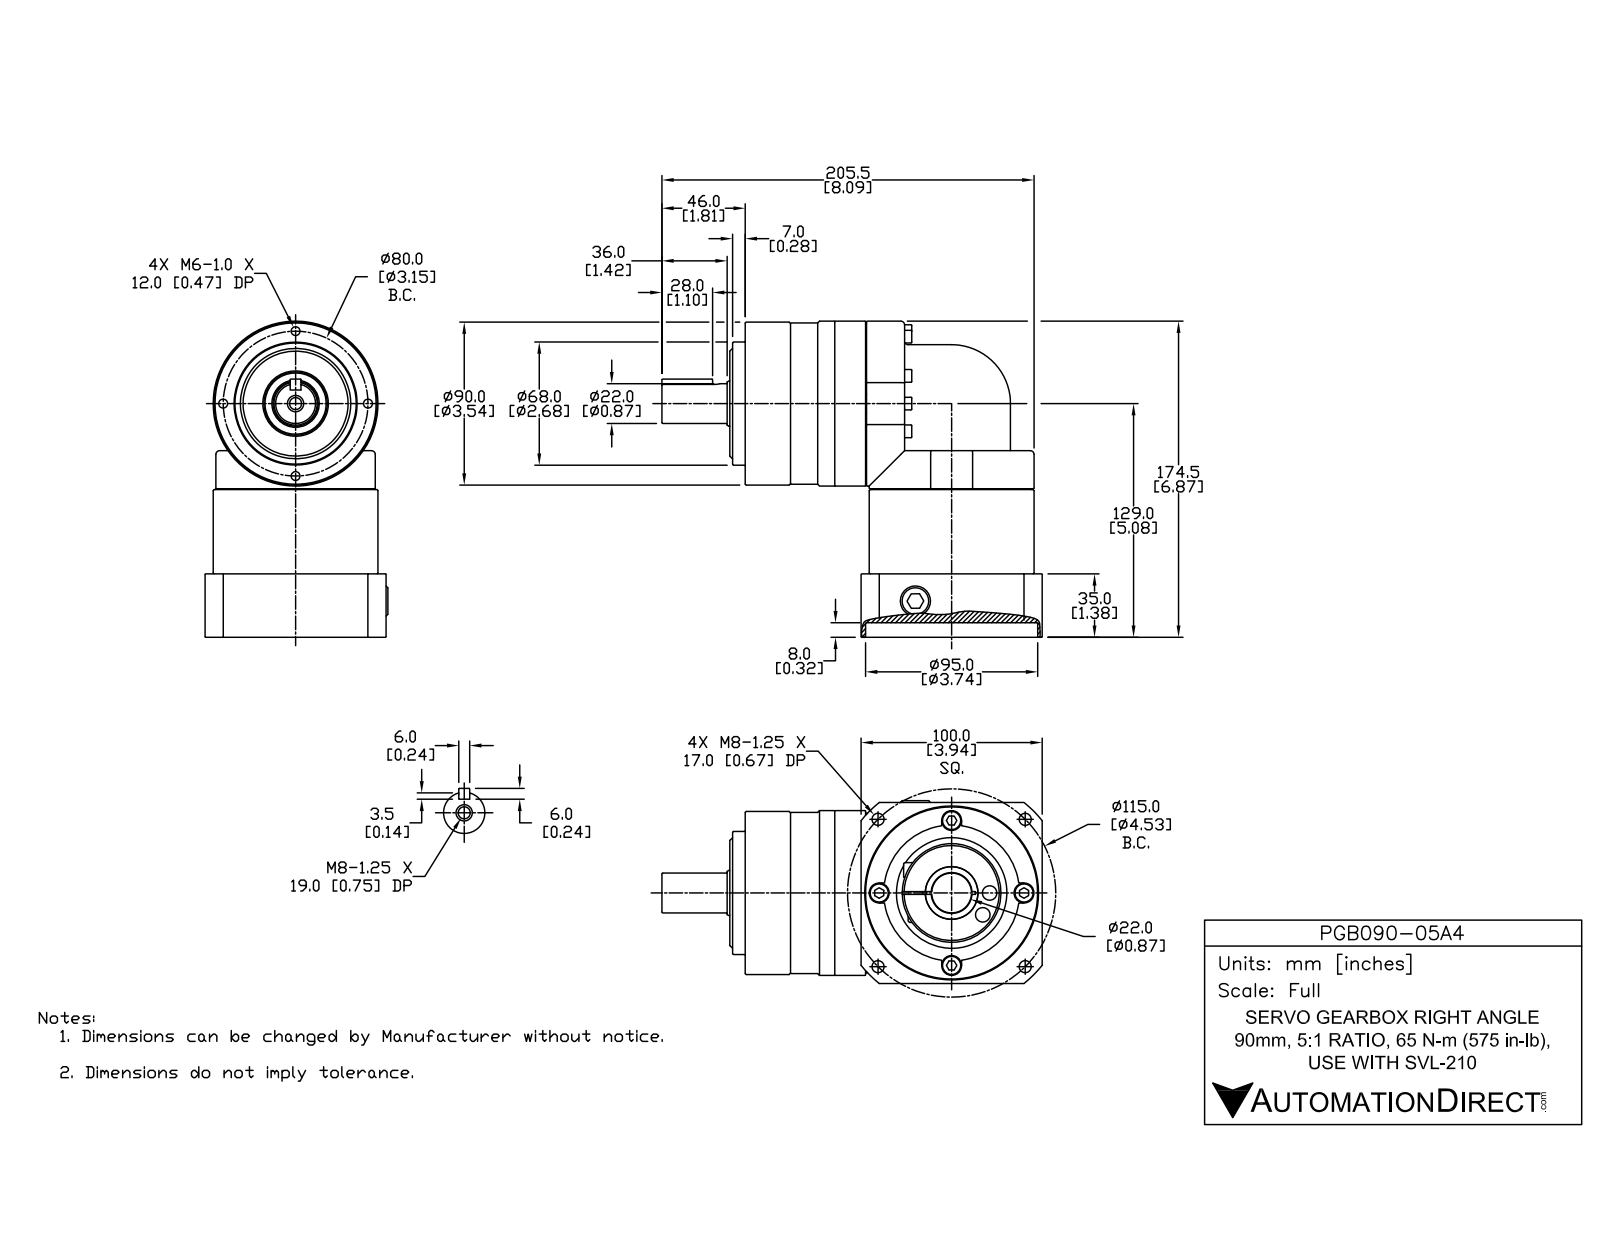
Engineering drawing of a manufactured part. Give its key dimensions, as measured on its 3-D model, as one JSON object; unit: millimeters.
{"part_name": "PGB090-05A4", "step_written_by": "SolidWorks 2014 (AUTOMOTIVE_DESIGN)", "units": "millimeters", "bodies": {"solids": 1, "faces": 511, "planar": 216, "cylindrical": 130, "other": 165}, "overall_size": [210, 174.5, 101], "volume_mm3": 1389000, "surface_area_mm2": 122500, "round_holes": [[4.9, 4], [6.7, 4], [11, 4], [8, 2], [6.7, 1], [8.8, 1], [14.2, 1], [22, 1], [61, 1], [75, 1], [95, 1]], "round_bosses_or_shafts": [[7, 9], [10, 4], [91, 2], [88, 2], [90, 1], [89, 1], [68, 1], [54.5, 1]], "partial_cylinders_radius": [[2, 6], [32.5, 2], [3, 1], [3.3, 1], [7, 1], [64, 1]], "face_to_face_distances": [100, 7, 28, 27, 8, 164, 64, 95, 35, 17.5], "hole_center_spacings": [40, 40.7, 56.6, 90.3, 57.5, 80, 81.3, 21]}
